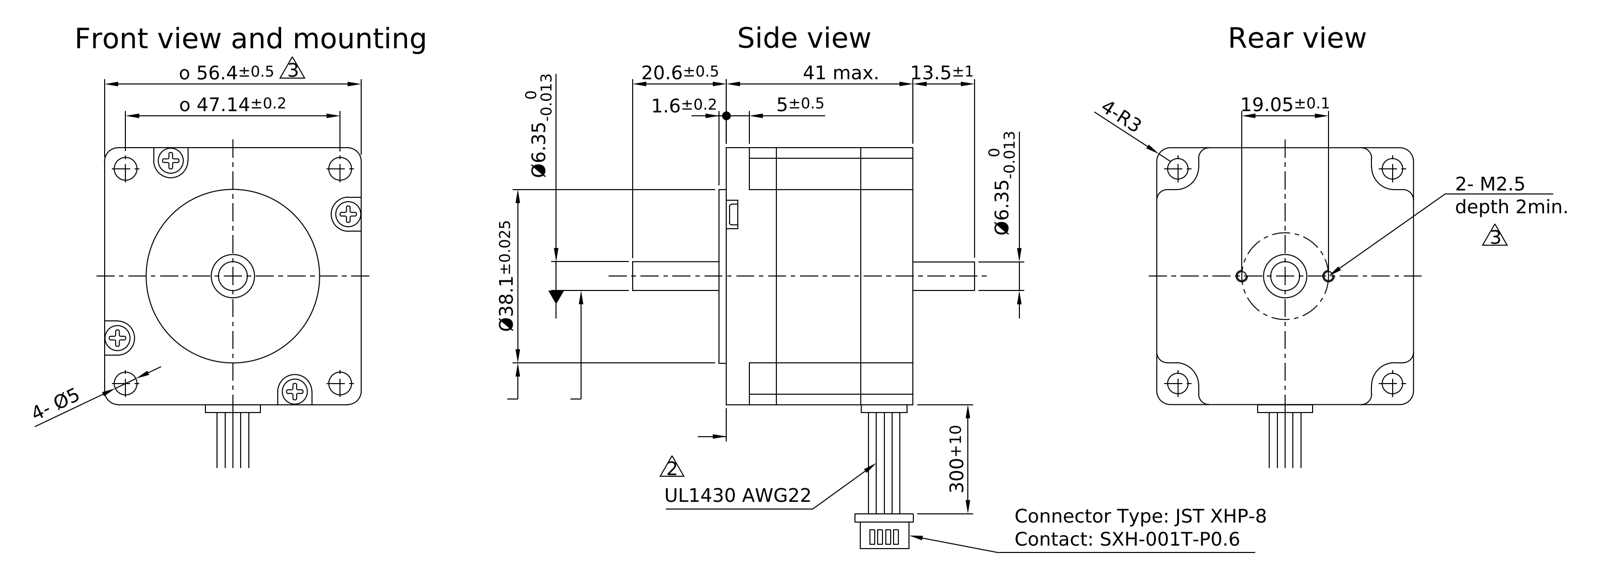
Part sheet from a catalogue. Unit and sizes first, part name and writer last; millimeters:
Units: millimetres
Overall size (bounding box): 75.1 × 73.37 × 56.94
Round holes (diameter × count): ⌀3.2 ×4, ⌀5 ×4, ⌀2.01 ×2, ⌀1 ×1, ⌀10 ×1
Round bosses / shafts (diameter × count): ⌀1 ×8, ⌀3 ×4, ⌀2.75 ×4, ⌀38.1 ×1, ⌀6.35 ×1
Partial cylindrical surfaces — rounded edges, fillets, slot ends (radius × count): R2.3 ×8, R3 ×4, R3.75 ×4, R5 ×4
Main face-to-face distances: 18, 12, 30, 56.4, 41, 29, 11, 42.6, 30.6, 12.6
Hole centre spacings: 7.95, 27.43, 30, 33.33, 39.47, 40.63, 42.43, 47.14
Volume: 120 498 mm³ · Surface area: 29 418 mm²
Bodies: 17 solids, 318 faces (160 planar, 88 cylindrical, 70 other)
Part name (STEP PRODUCT): ST5918X1008-B
STEP written by: Autodesk Inventor 2017 (AUTOMOTIVE_DESIGN)
